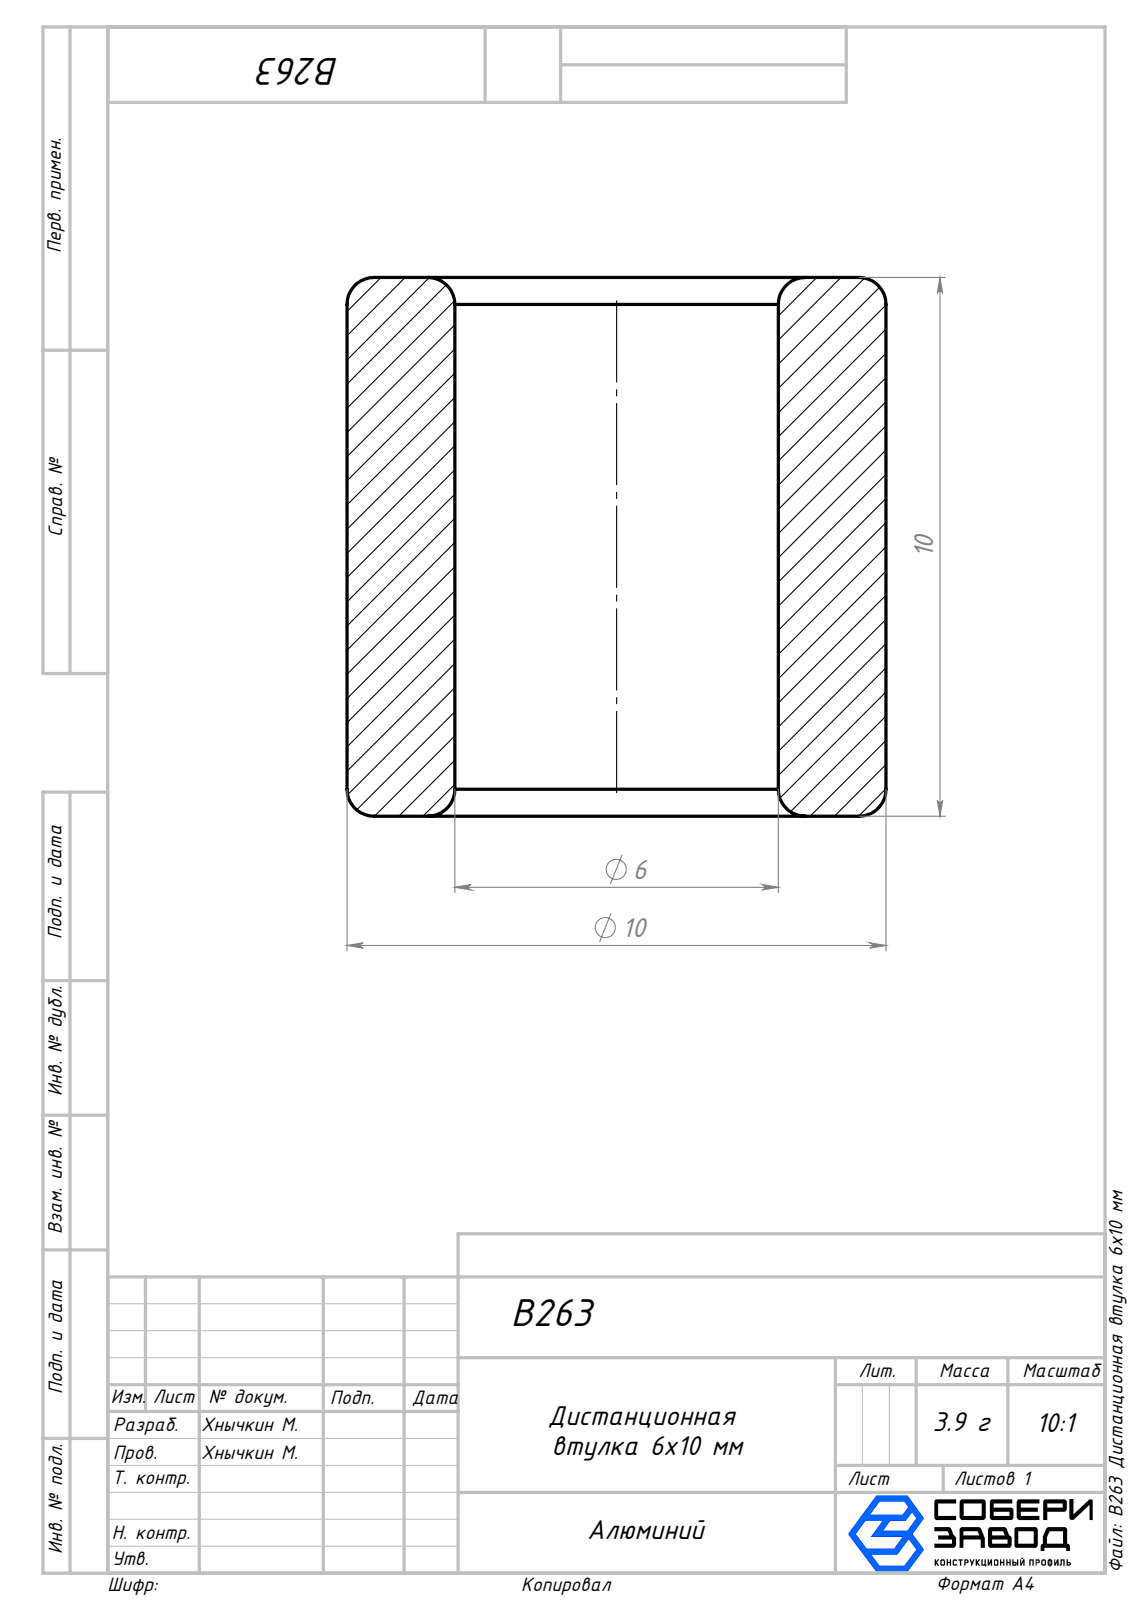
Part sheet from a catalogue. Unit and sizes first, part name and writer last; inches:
Units: inches
Overall size (bounding box): 0.394 × 0.394 × 0.394
Round holes (diameter × count): ⌀0.236 ×1
Round bosses / shafts (diameter × count): ⌀0.394 ×1
Main face-to-face distances: 0.394
Volume: 0.03 in³ · Surface area: 0.902 in²
Bodies: 1 solid, 14 faces (2 planar, 4 cylindrical, 8 other)
Part name (STEP PRODUCT): B263 Дистанционная втулка 6x10 мм
STEP written by: SolidWorks 2026 (AUTOMOTIVE_DESIGN)
